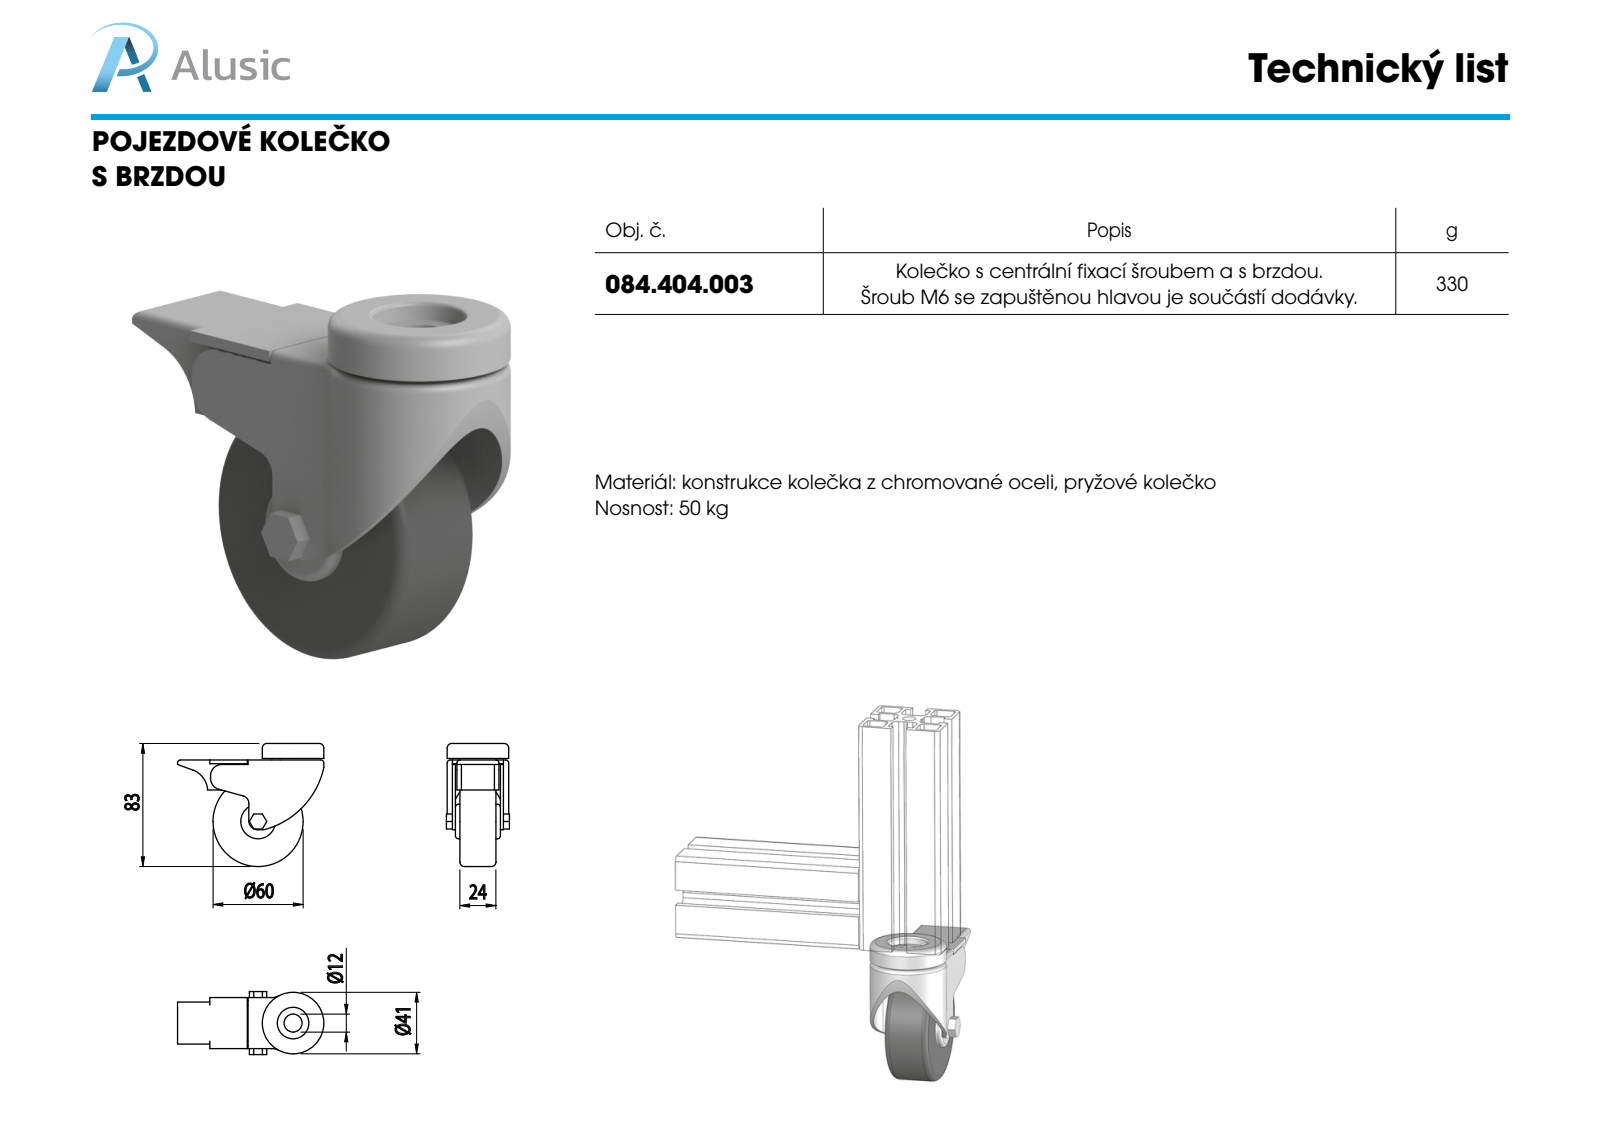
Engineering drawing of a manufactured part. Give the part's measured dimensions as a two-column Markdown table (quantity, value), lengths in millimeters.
| quantity | value |
| --- | --- |
| part name | 084.404.003 |
| STEP written by | SolidWorks 2011 (CONFIG_CONTROL_DESIGN) |
| units | millimeters |
| bodies | 7 solids, 122 faces (60 planar, 43 cylindrical, 19 other) |
| overall size | 97.5 × 82 × 42 |
| volume | 106 425 mm³ |
| surface area | 36 565 mm² |
| round holes (diameter × count) | 12 × 1, 21 × 1, 39 × 1 |
| round bosses / shafts (diameter × count) | 23 × 2, 60 × 1, 41 × 1 |
| partial cylindrical surfaces (radius × count) | 2 × 5, 6 × 2, 7.5 × 2, 10 × 2, 12 × 2, 5 × 1, 15 × 1, 18.49 × 1 |
| main face-to-face distances | 2, 3, 29, 27, 5, 32, 1, 24, 30, 26 |
